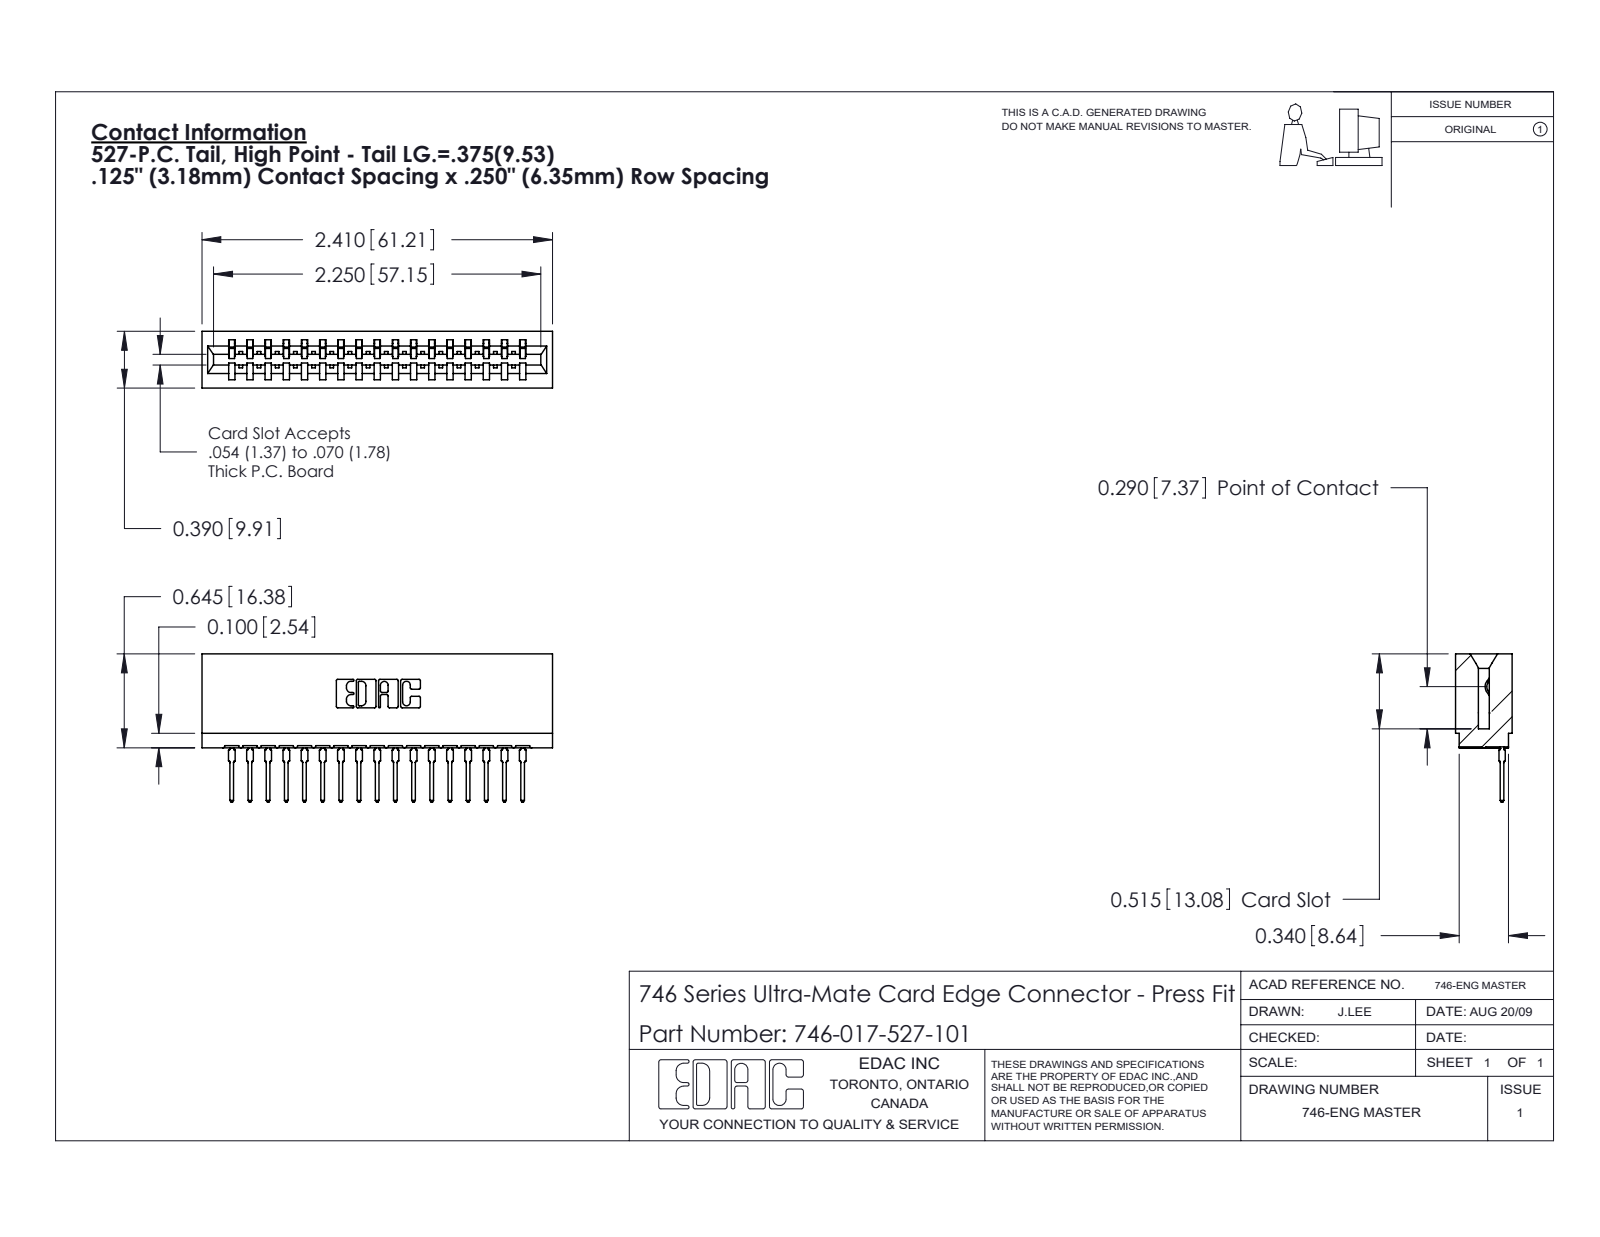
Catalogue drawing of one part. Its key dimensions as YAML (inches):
part_name: "746-017-527-101; 746 Part_.515 Slot Depth - 01; 746-292-001_527"
step_written_by: "SolidWorks 2020 (CONFIG_CONTROL_DESIGN)"
units: inches
bodies: {solids: 18, faces: 1933, planar: 1126, cylindrical: 365, other: 442}
overall_size: [2.41, 1.019, 0.39]
volume: 0.402
surface_area: 14.62
partial_cylinders:
  - {radius: 0.021, count: 34}
  - {radius: 0.01, count: 22}
  - {radius: 0.015, count: 18}
  - {radius: 0.007, count: 6}
  - {radius: 0.031, count: 6}
  - {radius: 0.005, count: 4}
  - {radius: 0.011, count: 4}
  - {radius: 0.026, count: 3}
face_to_face_distances: [0.25, 0.333, 0.057, 0.39, 0.5, 0.125, 0.125, 0.025, 0.307, 0.083]
